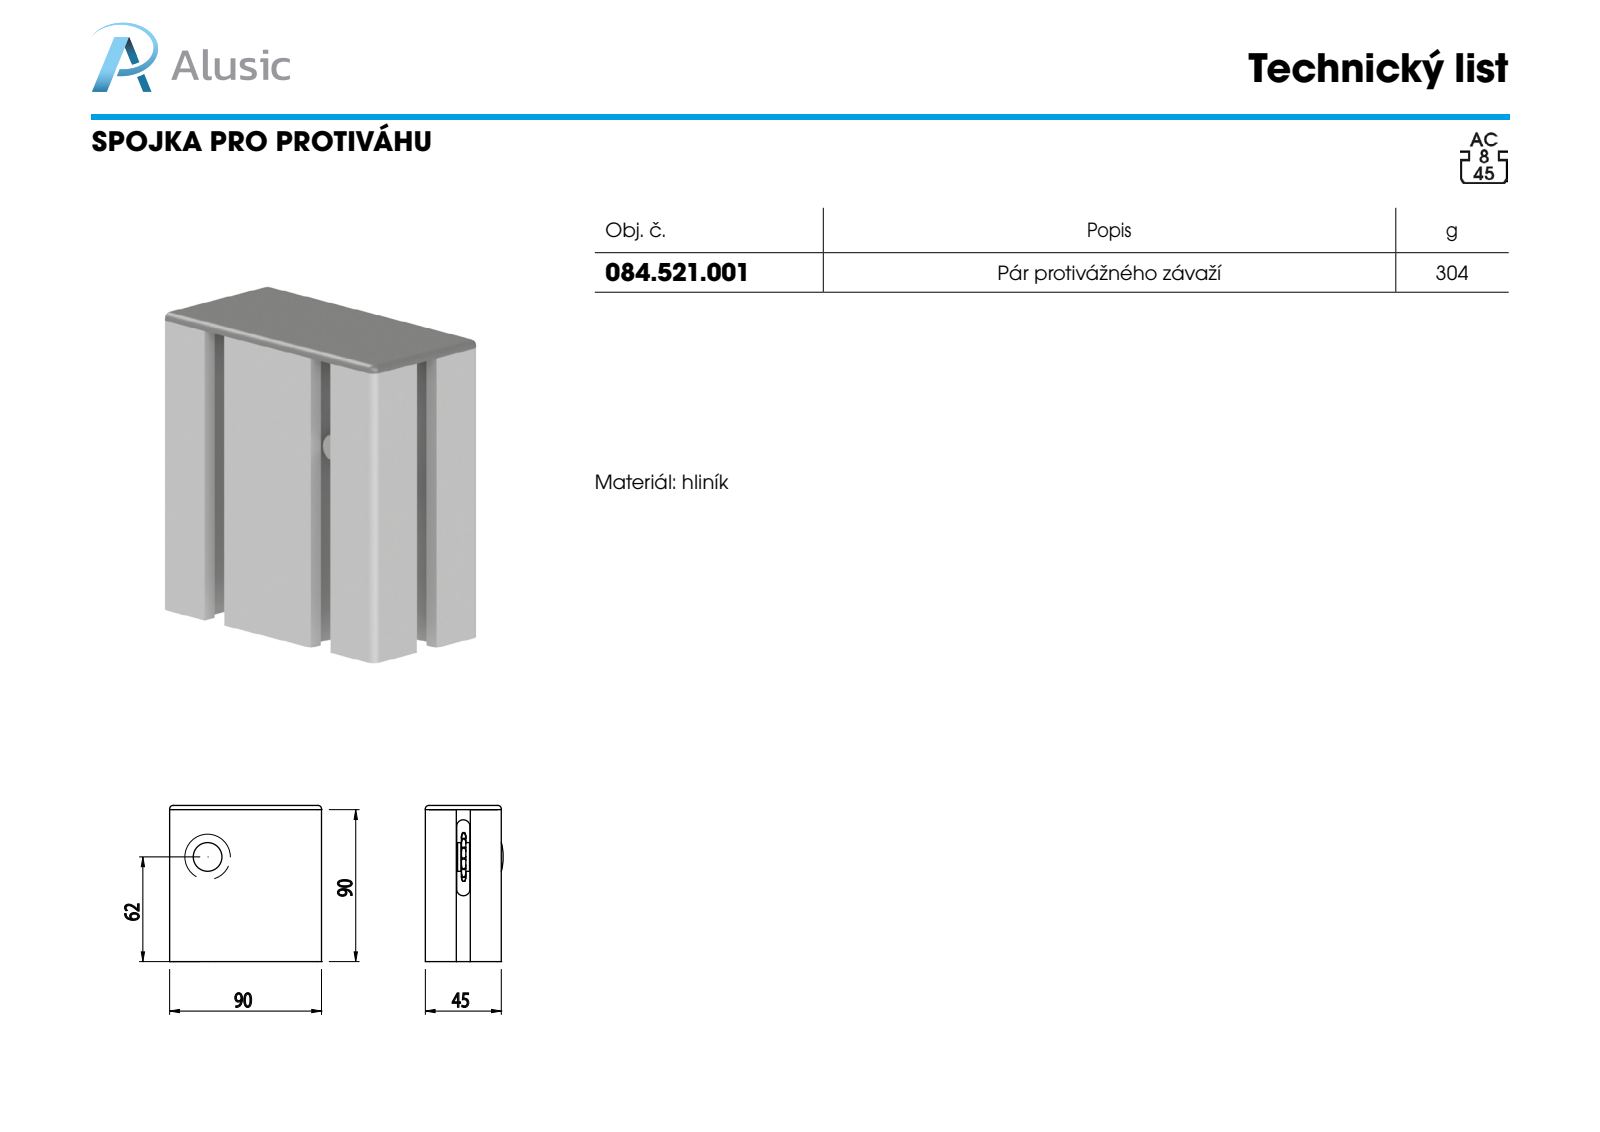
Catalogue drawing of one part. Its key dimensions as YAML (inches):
part_name: "70801b SX; 084.521.001; 084.202.005 SX; 084.201.019 SX (+5 more)"
step_written_by: "SolidWorks 2011 (CONFIG_CONTROL_DESIGN)"
units: inches
bodies: {solids: 8, faces: 326, planar: 102, cylindrical: 162, other: 62}
overall_size: [3.642, 3.543, 1.815]
volume: 6.331
surface_area: 142.7
round_holes:
  - {diameter: 0.374, count: 4}
  - {diameter: 0.287, count: 2}
  - {diameter: 0.268, count: 1}
  - {diameter: 0.311, count: 1}
  - {diameter: 0.315, count: 1}
  - {diameter: 0.472, count: 1}
  - {diameter: 0.512, count: 1}
  - {diameter: 0.52, count: 1}
round_bosses_or_shafts:
  - {diameter: 0.453, count: 4}
  - {diameter: 0.669, count: 1}
  - {diameter: 0.543, count: 1}
partial_cylinders:
  - {radius: 0.885, count: 28}
  - {radius: 0.039, count: 14}
  - {radius: 0.093, count: 14}
  - {radius: 0.118, count: 7}
  - {radius: 0.079, count: 4}
  - {radius: 0.098, count: 4}
  - {radius: 0.126, count: 4}
  - {radius: 0.157, count: 2}
face_to_face_distances: [0.071, 1.772, 1.224, 1.701, 1.154, 0.543, 0.098, 3.472, 2.319, 0.067]
hole_center_spacings: [0.781, 2.359, 1.181, 2.795, 3.035, 1.772]
